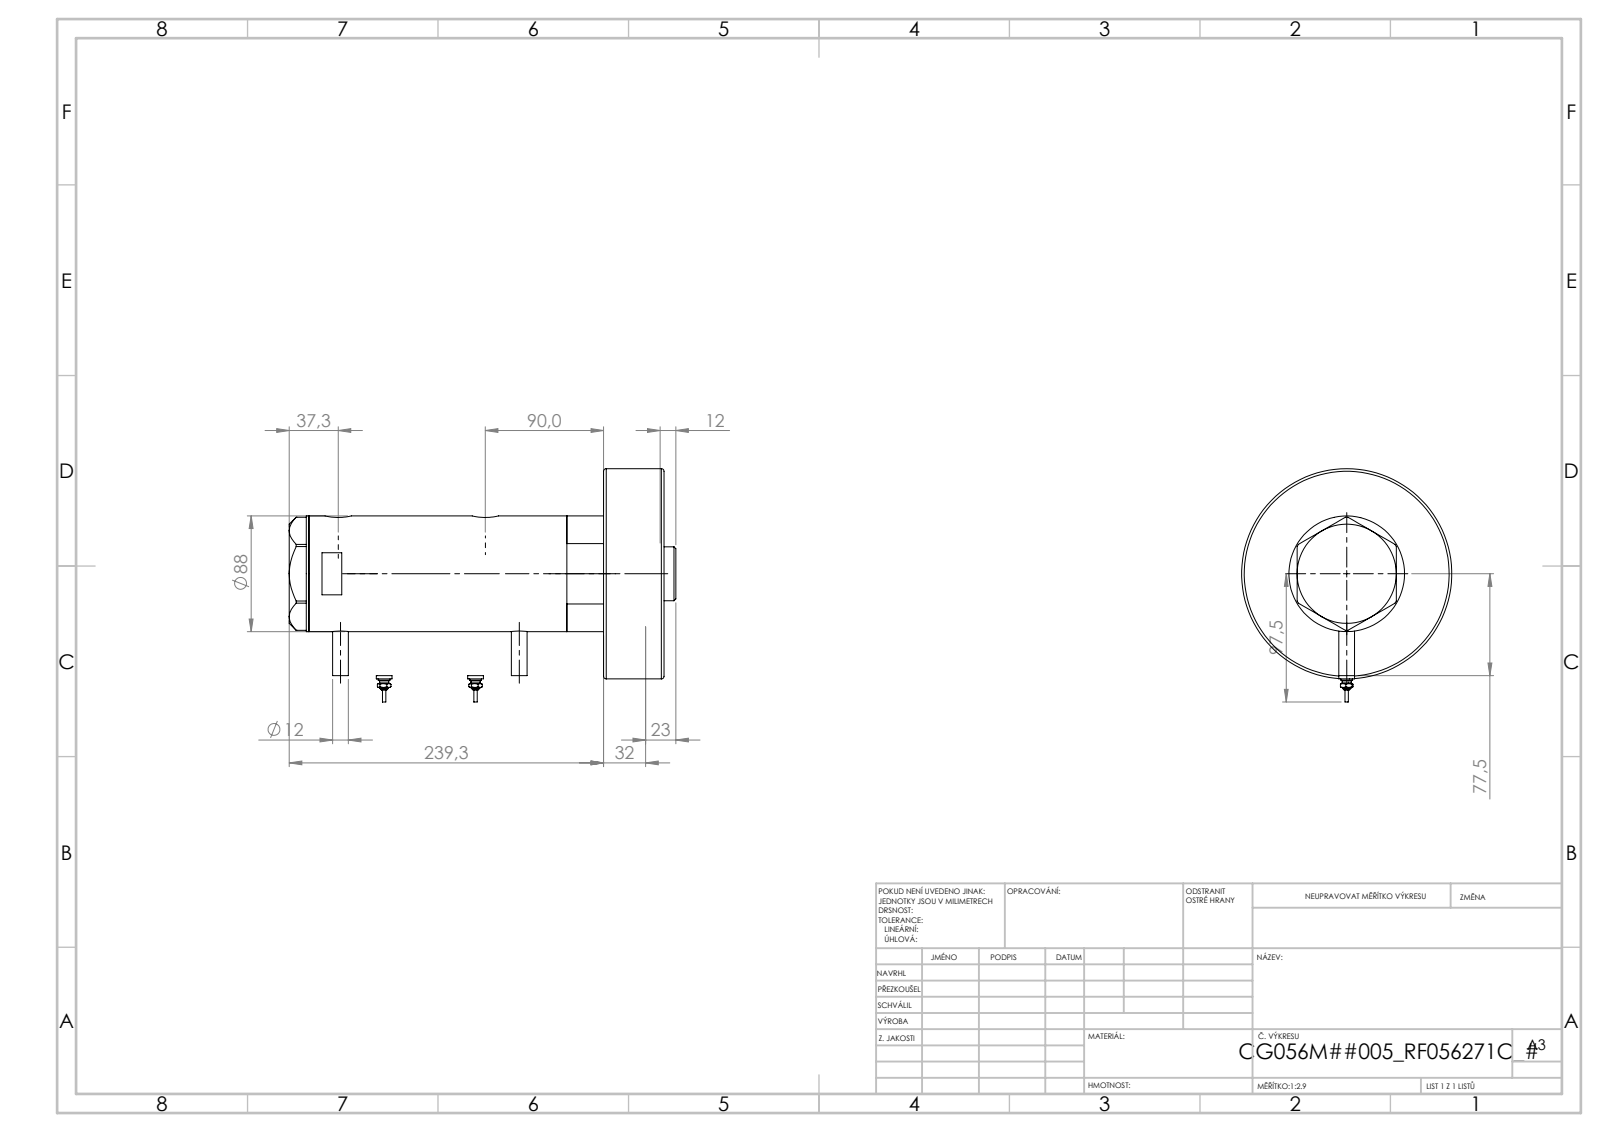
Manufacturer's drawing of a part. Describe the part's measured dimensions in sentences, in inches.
The part is named "V270CG_FRONT; V270CG_VC; V270CG_MIDDLE; V270CG_SWITCH (+2 more)". Its 3-D file was written by "SolidWorks 2019 (CONFIG_CONTROL_DESIGN)". It is 7 solids with 242 faces: 83 planar, 81 cylindrical and 78 other. Overall it measures 9.034 by 6.299 by 6.299 inches. Its volume is 116.6 cubic inches and its surface area 386.9 square inches. Round holes: 2 of diameter 0.197, 2 of diameter 0.492, 2 of diameter 0.518, 2 of diameter 0.787, 1 of diameter 0.571, 1 of diameter 1.654, 1 of diameter 1.713, 1 of diameter 2.205, 1 of diameter 2.362, 1 of diameter 2.953, 1 of diameter 3.15. Round bosses or shafts: 2 of diameter 0.472, 2 of diameter 0.354, 2 of diameter 0.276, 2 of diameter 0.171, 2 of diameter 0.094, 1 of diameter 6.299, 1 of diameter 3.465, 1 of diameter 2.874. The main face-to-face distances are 1.811, 6.177, 7.988, 3.126, 3.051, 4.862, 1.024, 2.102, 5.154, 6.965. The hole center spacings are 0.067, 1.016, 2.177, 2.244, 3.193, 3.26.
